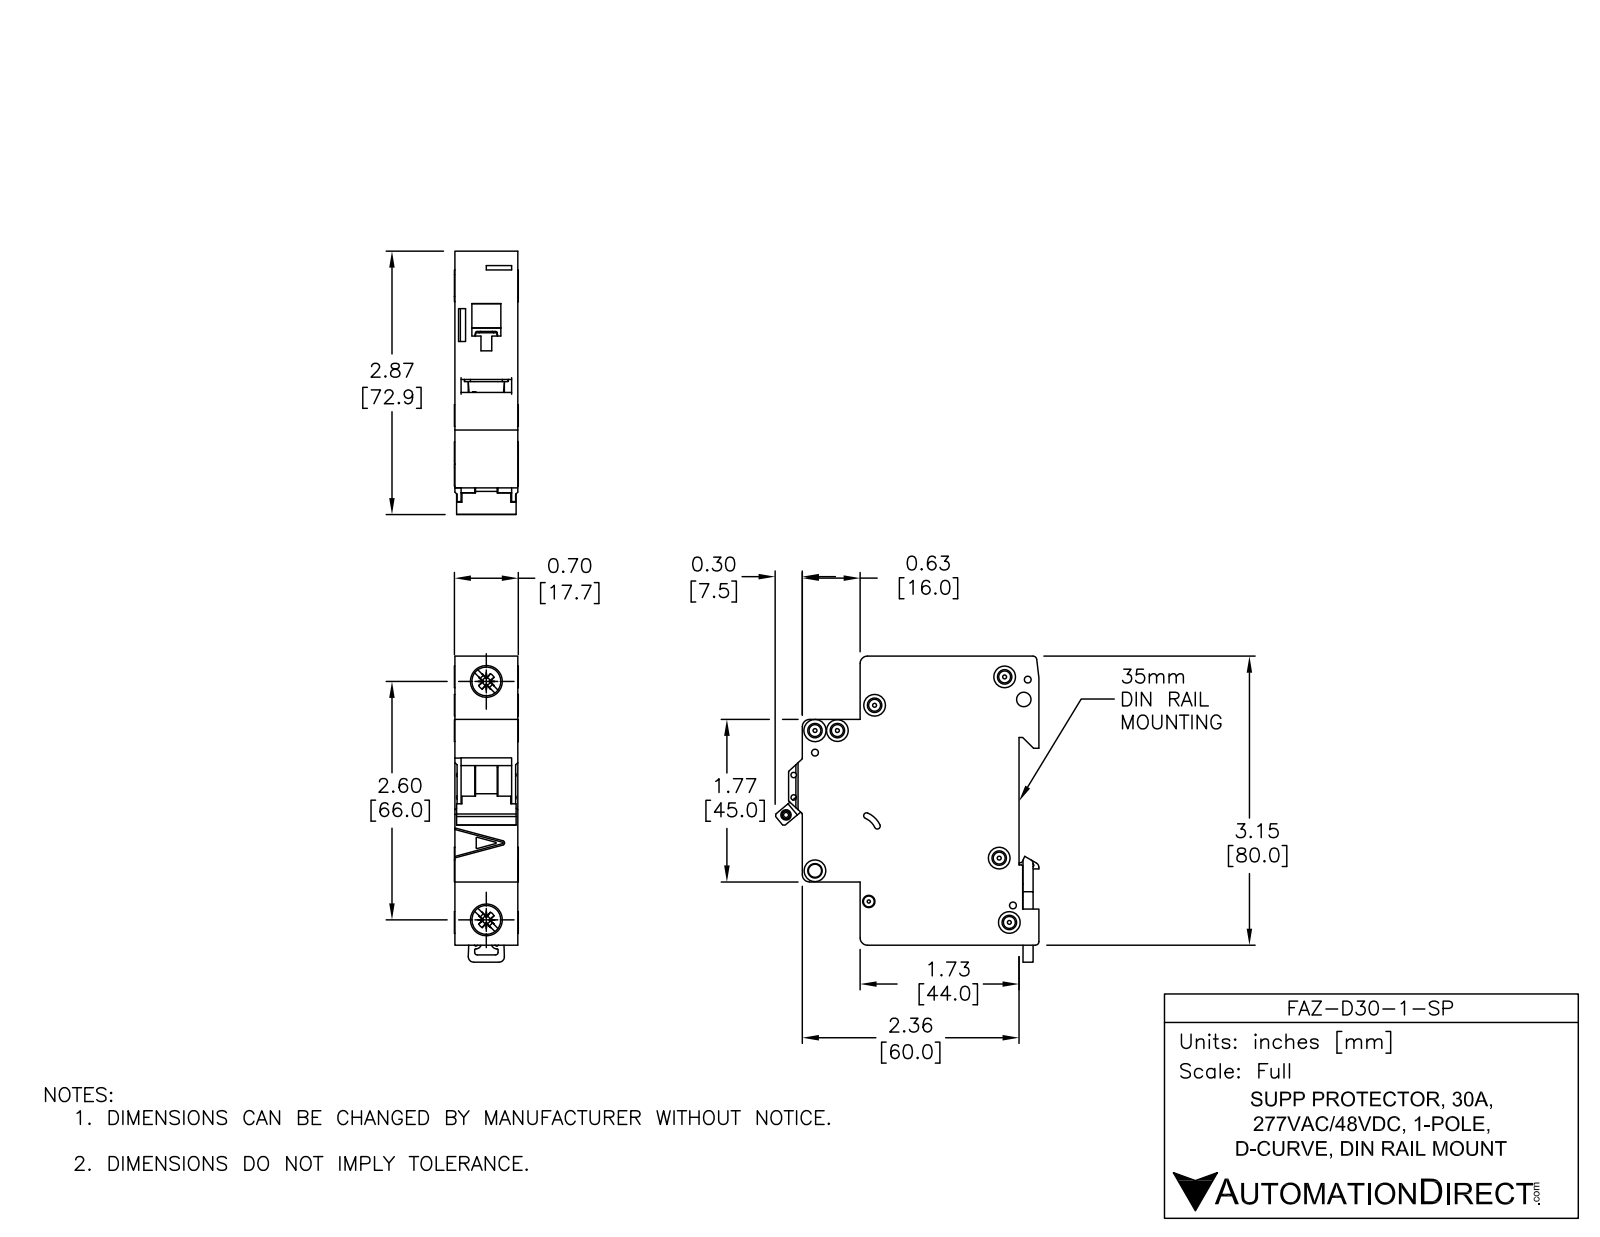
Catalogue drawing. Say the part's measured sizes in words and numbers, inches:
The part is named "FAZ-D30-1-SP". Its 3-D file was written by "SolidWorks 2014 (AUTOMOTIVE_DESIGN)". It is 5 solids with 558 faces: 235 planar, 202 cylindrical and 121 other. Overall it measures 3.338 by 2.876 by 0.697 inches. Its volume is 4.573 cubic inches and its surface area 30.29 square inches. Round holes: 6 of diameter 0.142, 3 of diameter 0.075, 2 of diameter 0.043, 2 of diameter 0.059, 2 of diameter 0.157, 2 of diameter 0.281, 1 of diameter 0.085, 1 of diameter 0.087, 1 of diameter 0.1, 1 of diameter 0.13, 1 of diameter 0.134. Round bosses or shafts: 4 of diameter 0.236, 2 of diameter 0.323, 1 of diameter 0.098. Partial cylindrical surfaces (rounded edges, fillets, slot ends): 30 of radius 0.01, 13 of radius 0.02, 8 of radius 0.079, 5 of radius 0.008, 4 of radius 0.039, 2 of radius 0.031, 2 of radius 0.118, 1 of radius 0.059. The main face-to-face distances are 0.689, 3.129, 0.217, 1.949, 1.732, 2.579, 2.362, 0.63, 0.069, 0.62. The hole center spacings are 0.244, 0.537, 0.189, 0.204, 0.221, 0.24, 0.254, 0.322.
